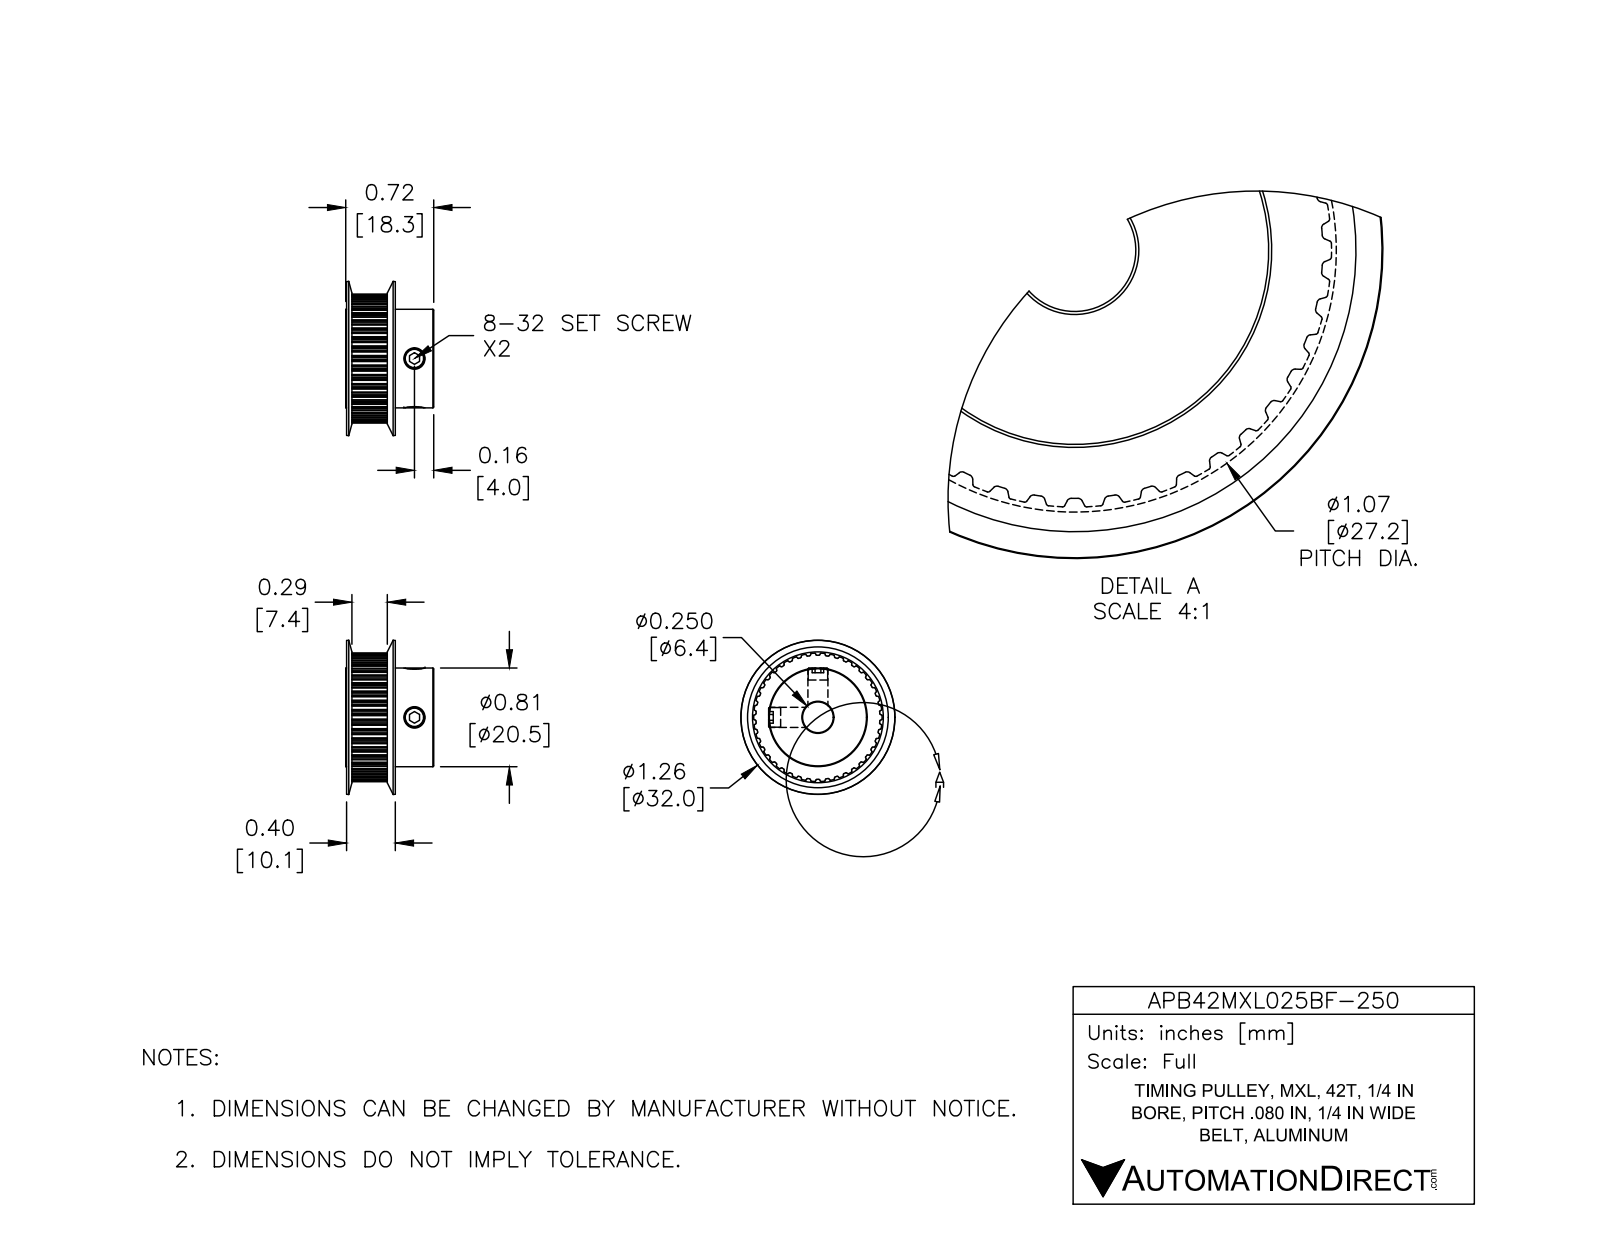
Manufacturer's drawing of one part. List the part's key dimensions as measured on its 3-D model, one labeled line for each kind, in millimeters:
Part name (STEP PRODUCT): APB42MXL025BF-250
STEP written by: SolidWorks 2016 (AUTOMOTIVE_DESIGN)
Units: millimetres
Bodies: 3 solids, 429 faces (108 planar, 295 cylindrical, 26 other)
Overall size (bounding box): 32 × 32 × 18.3
Volume: 7 670 mm³ · Surface area: 4 179 mm²
Round holes (diameter × count): ⌀4.2 ×2, ⌀6.4 ×1
Round bosses / shafts (diameter × count): ⌀4.1 ×2, ⌀20.5 ×1
Partial cylindrical surfaces — rounded edges, fillets, slot ends (radius × count): R0.1 ×84, R0.2 ×84, R12.9 ×1, R13.3 ×1
Main face-to-face distances: 9.2, 0.6, 9.8, 18.3, 17.6, 8.4, 8.6, 8, 1.2, 9.6
